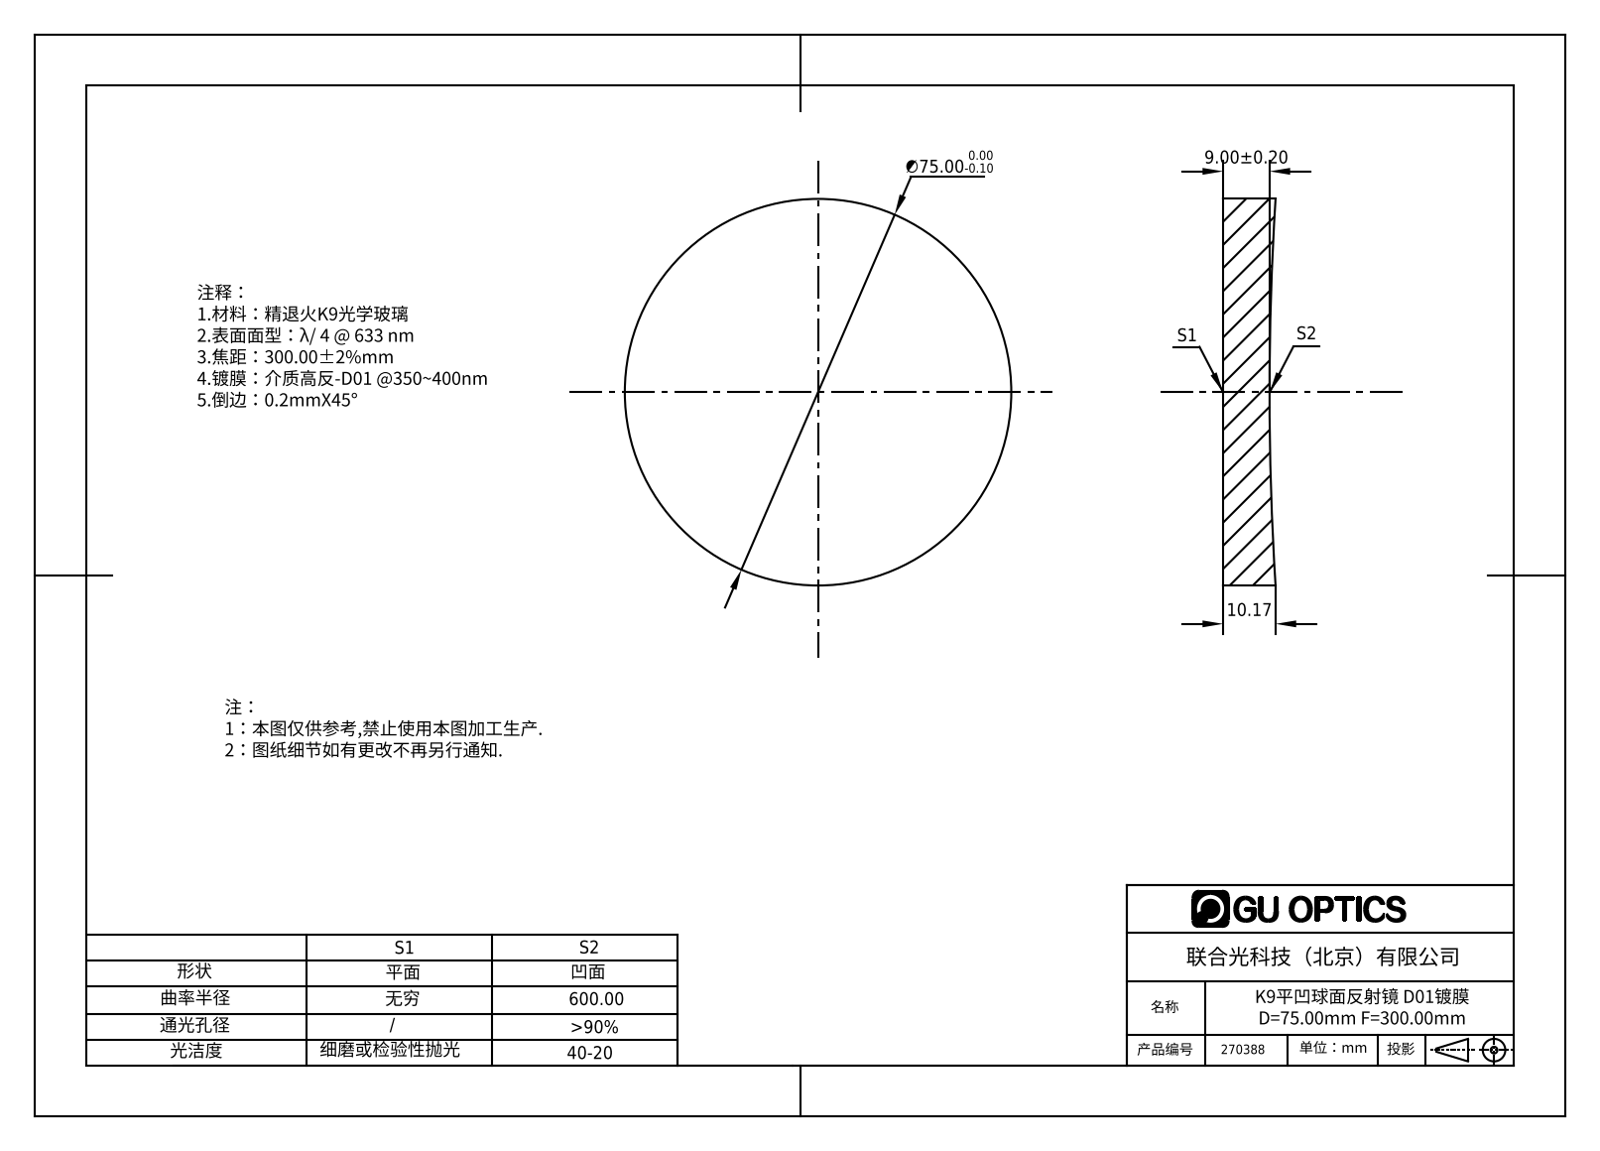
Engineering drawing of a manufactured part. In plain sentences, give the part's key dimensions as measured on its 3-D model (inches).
The part is named "270063". Its 3-D file was written by "SolidWorks 2016 (AUTOMOTIVE_DESIGN)". It is 1 solid with 5 faces: 1 planar, 2 cylindrical and 2 other. Overall it measures 2.953 by 2.953 by 0.4 inches. Its volume is 2.584 cubic inches and its surface area 17.42 square inches. Round bosses or shafts: 1 of diameter 2.953.
